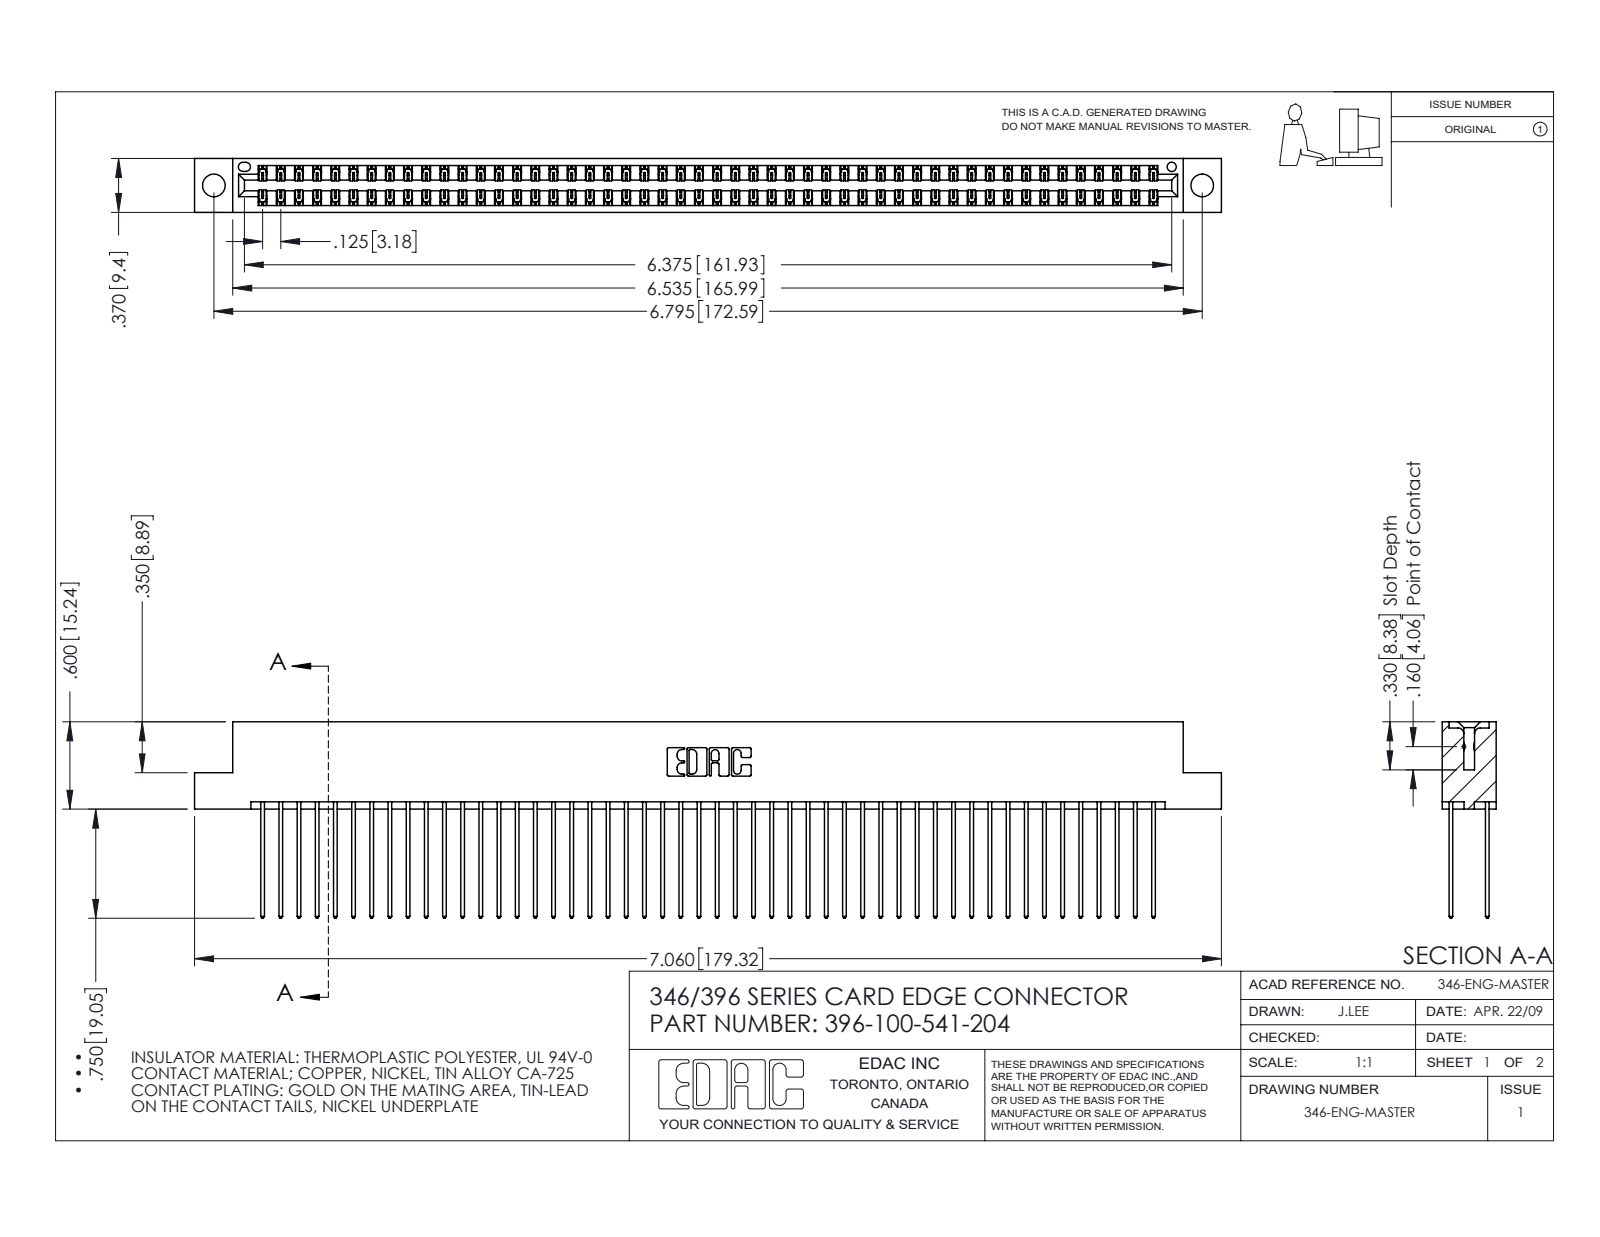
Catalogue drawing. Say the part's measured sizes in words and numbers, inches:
The part is named "345-292-001_345-293-141; 396-100-541-204; 346 Part_Flush Mounting Lugs - 0.156 Dia-TH". Its 3-D file was written by "SolidWorks 2016 (CONFIG_CONTROL_DESIGN)". It is 101 solids with 5322 faces: 3576 planar, 1746 cylindrical and 0 other. Overall it measures 7.06 by 1.35 by 0.37 inches. Its volume is 1.101 cubic inches and its surface area 42.59 square inches. Round holes: 2 of diameter 0.156, 1 of diameter 0.064. Partial cylindrical surfaces (rounded edges, fillets, slot ends): 150 of radius 0.006, 100 of radius 0.01, 22 of radius 0.01, 6 of radius 0.007, 6 of radius 0.031, 3 of radius 0.026, 2 of radius 0.014, 2 of radius 0.022. The main face-to-face distances are 0.048, 0.322, 0.25, 0.072, 0.298, 0.025, 0.37, 0.275, 0.225, 0.148. The hole center spacings are 0.246, 6.586, 6.795.
